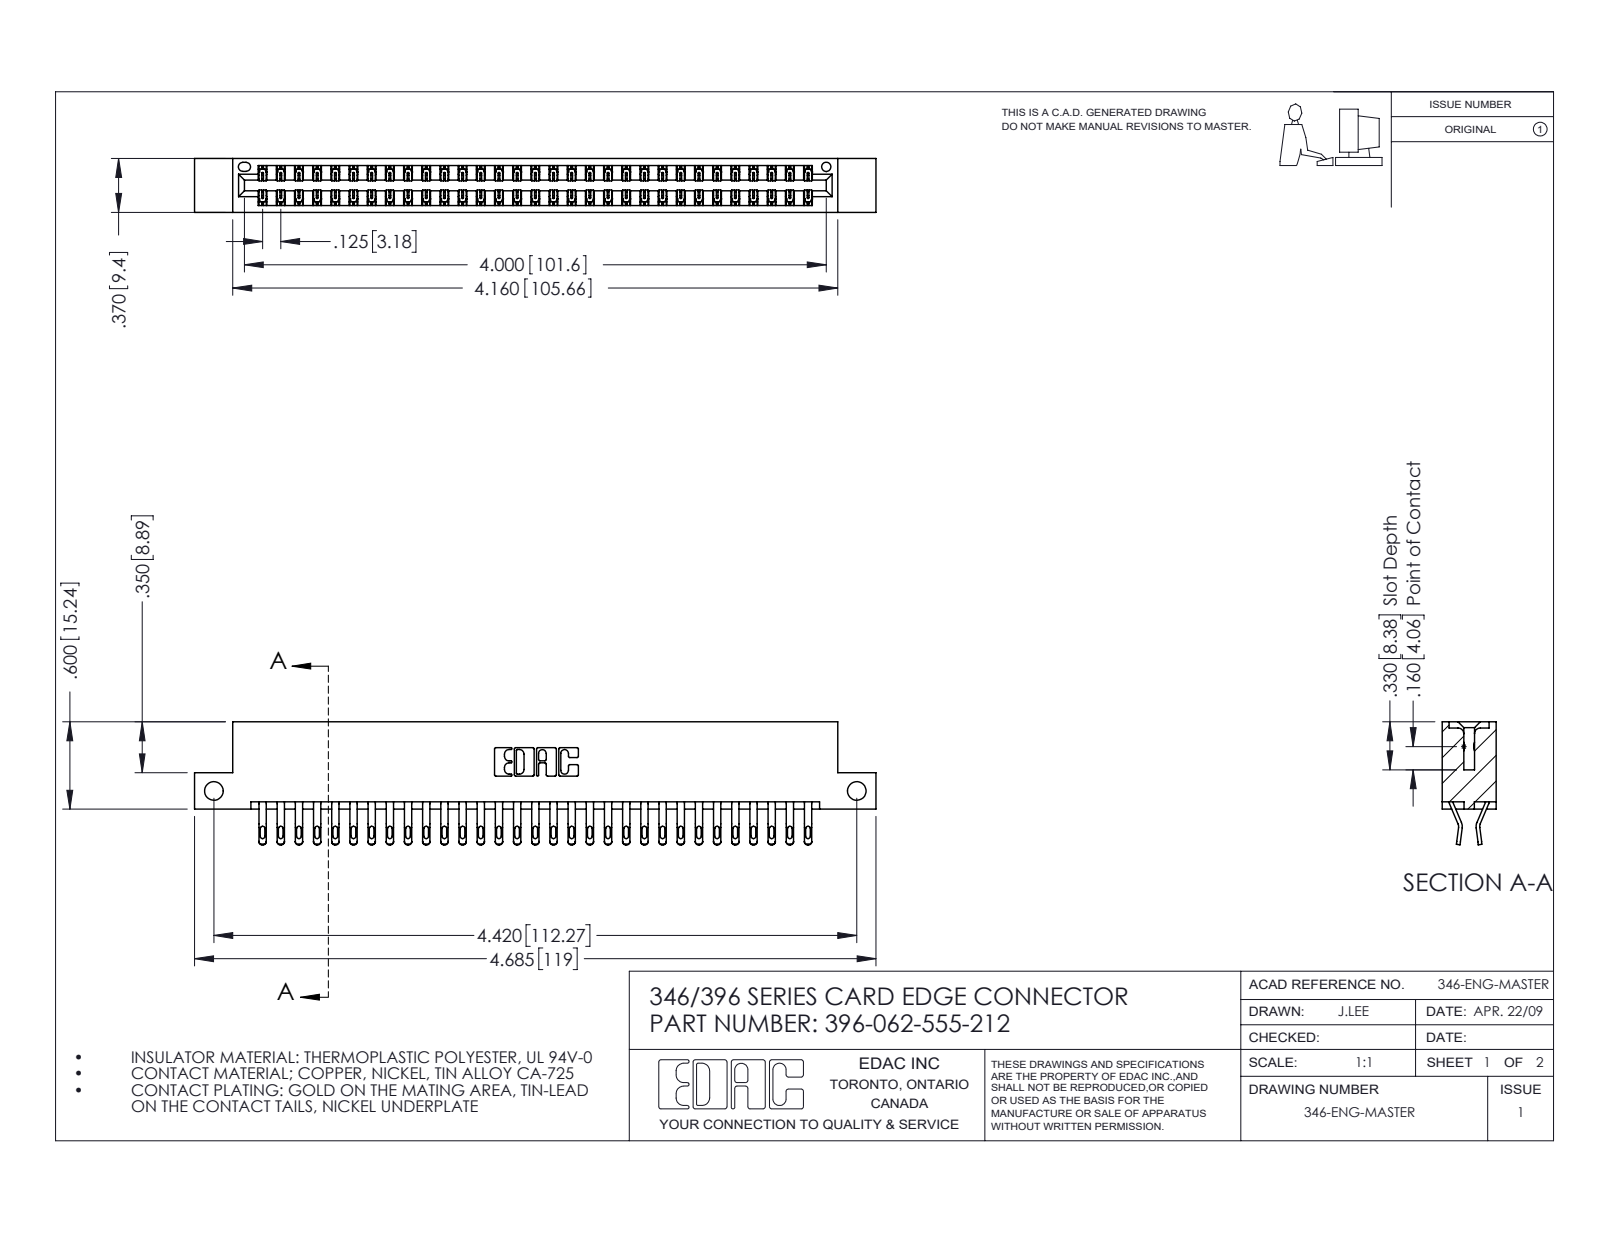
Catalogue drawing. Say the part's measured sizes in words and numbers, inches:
The part is named "396-062-555-212; 346 Part_Flush Mounting Lugs - Side Mount; 345-292-001_555 Tail". Its 3-D file was written by "SolidWorks 2016 (CONFIG_CONTROL_DESIGN)". It is 63 solids with 3718 faces: 2122 planar, 1596 cylindrical and 0 other. Overall it measures 4.685 by 0.845 by 0.37 inches. Its volume is 0.709 cubic inches and its surface area 25.25 square inches. Round holes: 2 of diameter 0.128, 1 of diameter 0.064. Partial cylindrical surfaces (rounded edges, fillets, slot ends): 124 of radius 0.016, 124 of radius 0.02, 93 of radius 0.006, 22 of radius 0.01, 6 of radius 0.007, 6 of radius 0.031, 3 of radius 0.026, 2 of radius 0.01. The main face-to-face distances are 0.048, 0.322, 0.37, 0.25, 0.025, 0.072, 0.298, 0.275, 0.148, 0.222. The hole center spacings are 4.42.
